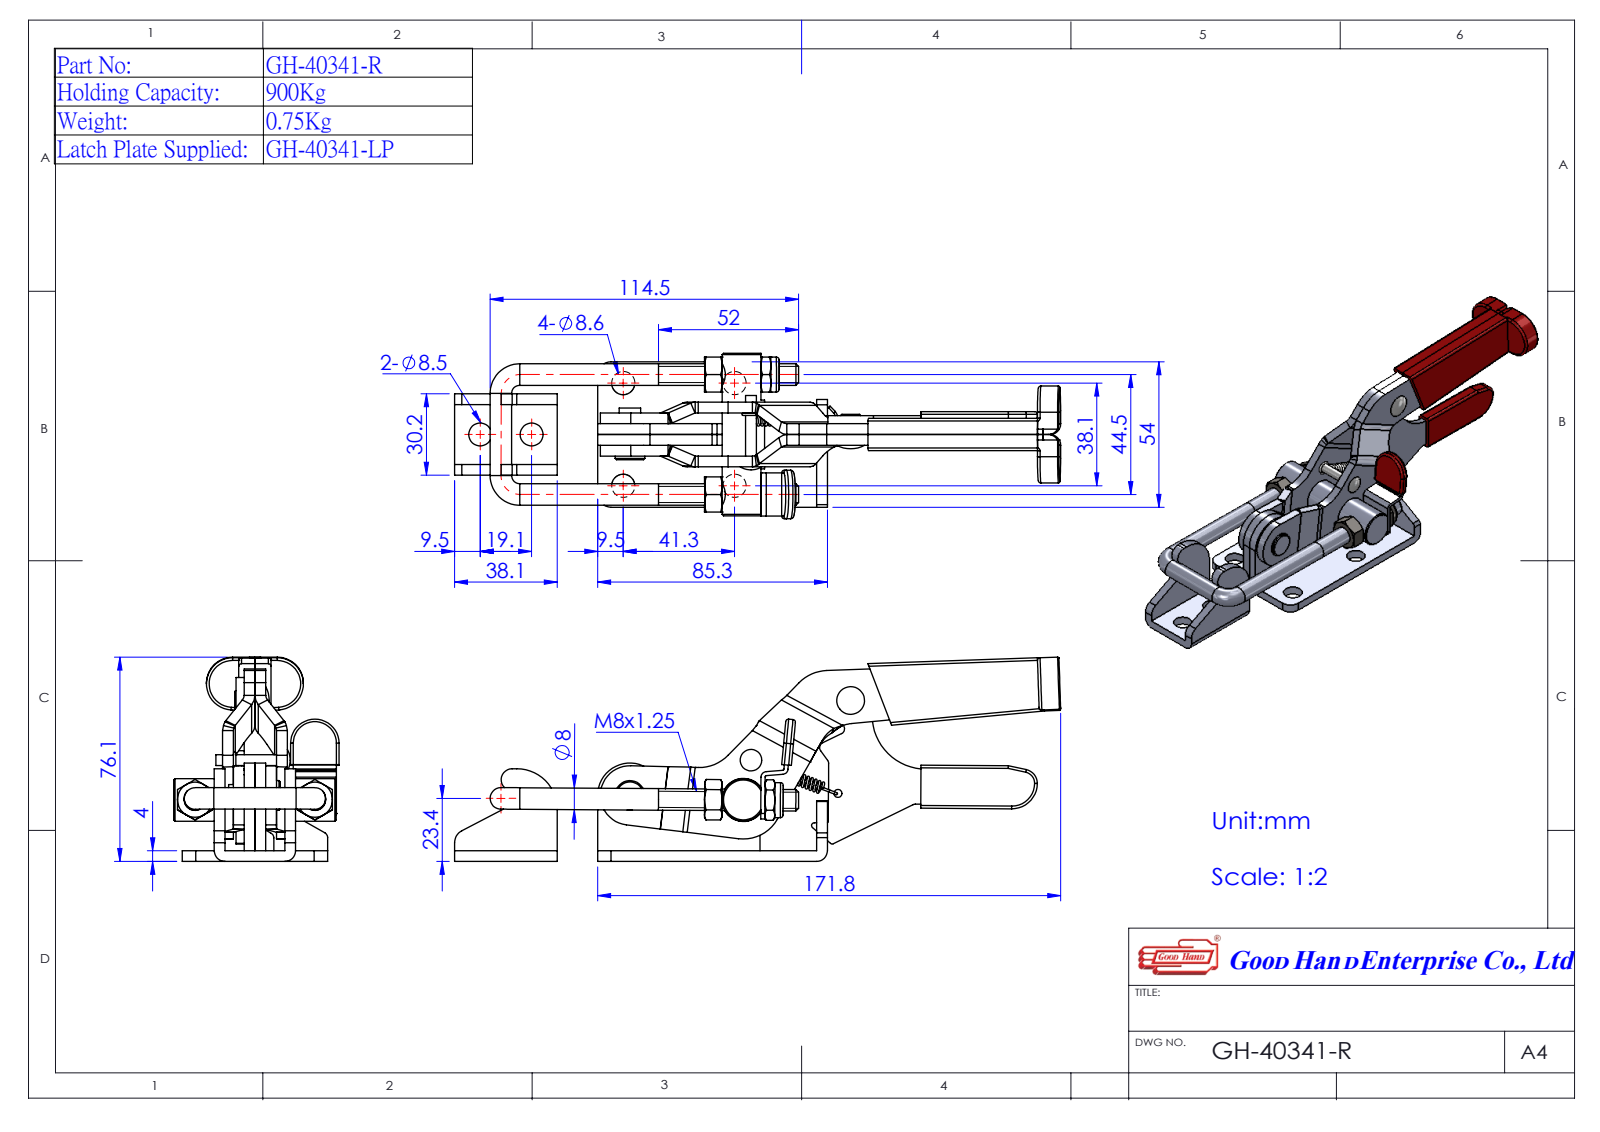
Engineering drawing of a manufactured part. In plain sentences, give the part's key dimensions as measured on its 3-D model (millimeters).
The part is named "14034144-1^GH-40341-R(簡化); GH-40341-R(簡化); Group5^GH-40341-R(簡化); Group2^GH-40341-R(簡化) (+2 more)". Its 3-D file was written by "SolidWorks 2016 (AUTOMOTIVE_DESIGN)". It is 8 solids with 455 faces: 205 planar, 149 cylindrical and 101 other. Overall it measures 225.03 by 75.85 by 61.4 millimeters. Its volume is 112 863 cubic millimeters and its surface area 56 128 square millimeters. Round holes: 5 of diameter 8, 4 of diameter 6.8, 4 of diameter 8.6, 3 of diameter 8.3, 2 of diameter 8.5, 2 of diameter 9.43, 1 of diameter 6, 1 of diameter 6.35, 1 of diameter 15.8. Round bosses or shafts: 3 of diameter 8, 2 of diameter 13, 1 of diameter 11, 1 of diameter 6.3. Partial cylindrical surfaces (rounded edges, fillets, slot ends): 8 of radius 5, 6 of radius 2, 6 of radius 15, 5 of radius 9, 4 of radius 0.1, 4 of radius 4.1, 3 of radius 0.5, 2 of radius 1. The main face-to-face distances are 4, 2, 8, 12, 16, 23.1, 3.1, 7.1, 19.1, 1. The hole center spacings are 44.5, 38.1, 38.97, 41.3, 56.19, 56.41, 77.67, 96.3.
